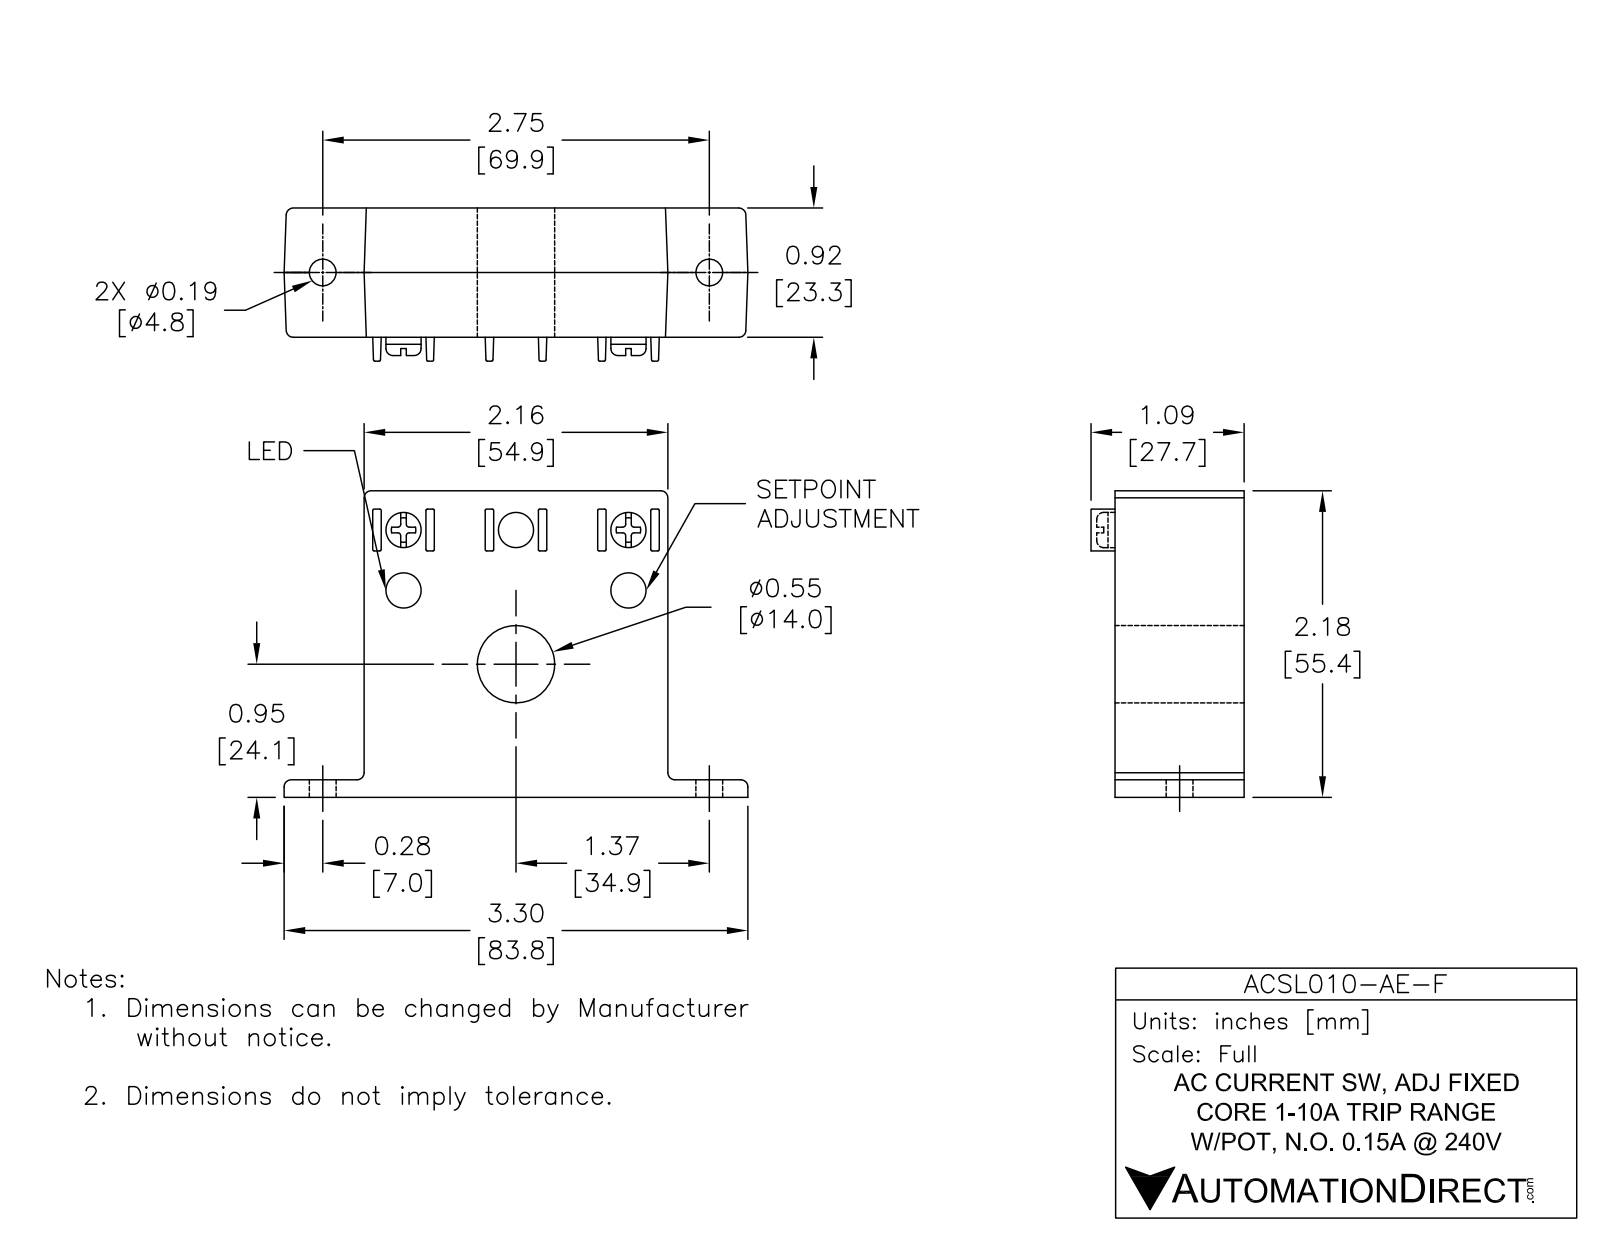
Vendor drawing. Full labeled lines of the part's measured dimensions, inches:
Part name (STEP PRODUCT): ACSL010-AE-F
STEP written by: SolidWorks 2018 (AUTOMOTIVE_DESIGN)
Units: inches
Bodies: 10 solids, 368 faces (236 planar, 114 cylindrical, 18 other)
Overall size (bounding box): 3.292 × 2.188 × 1.151
Volume: 4.41 in³ · Surface area: 30.46 in²
Round holes (diameter × count): ⌀0.2 ×4, ⌀0.121 ×2, ⌀0.13 ×2, ⌀0.14 ×2, ⌀0.24 ×2, ⌀0.55 ×1, ⌀0.59 ×1
Round bosses / shafts (diameter × count): ⌀0.321 ×2, ⌀0.138 ×2, ⌀0.187 ×1, ⌀0.063 ×1
Partial cylindrical surfaces — rounded edges, fillets, slot ends (radius × count): R0.015 ×14, R0.089 ×1
Main face-to-face distances: 0.937, 0.938, 2.188, 2.172, 0.145, 2.043, 0.383, 0.824, 1.03, 0.093
Hole centre spacings: 0.341, 1.647, 1.682, 0.015, 0.335, 1.034, 1.035, 1.036
